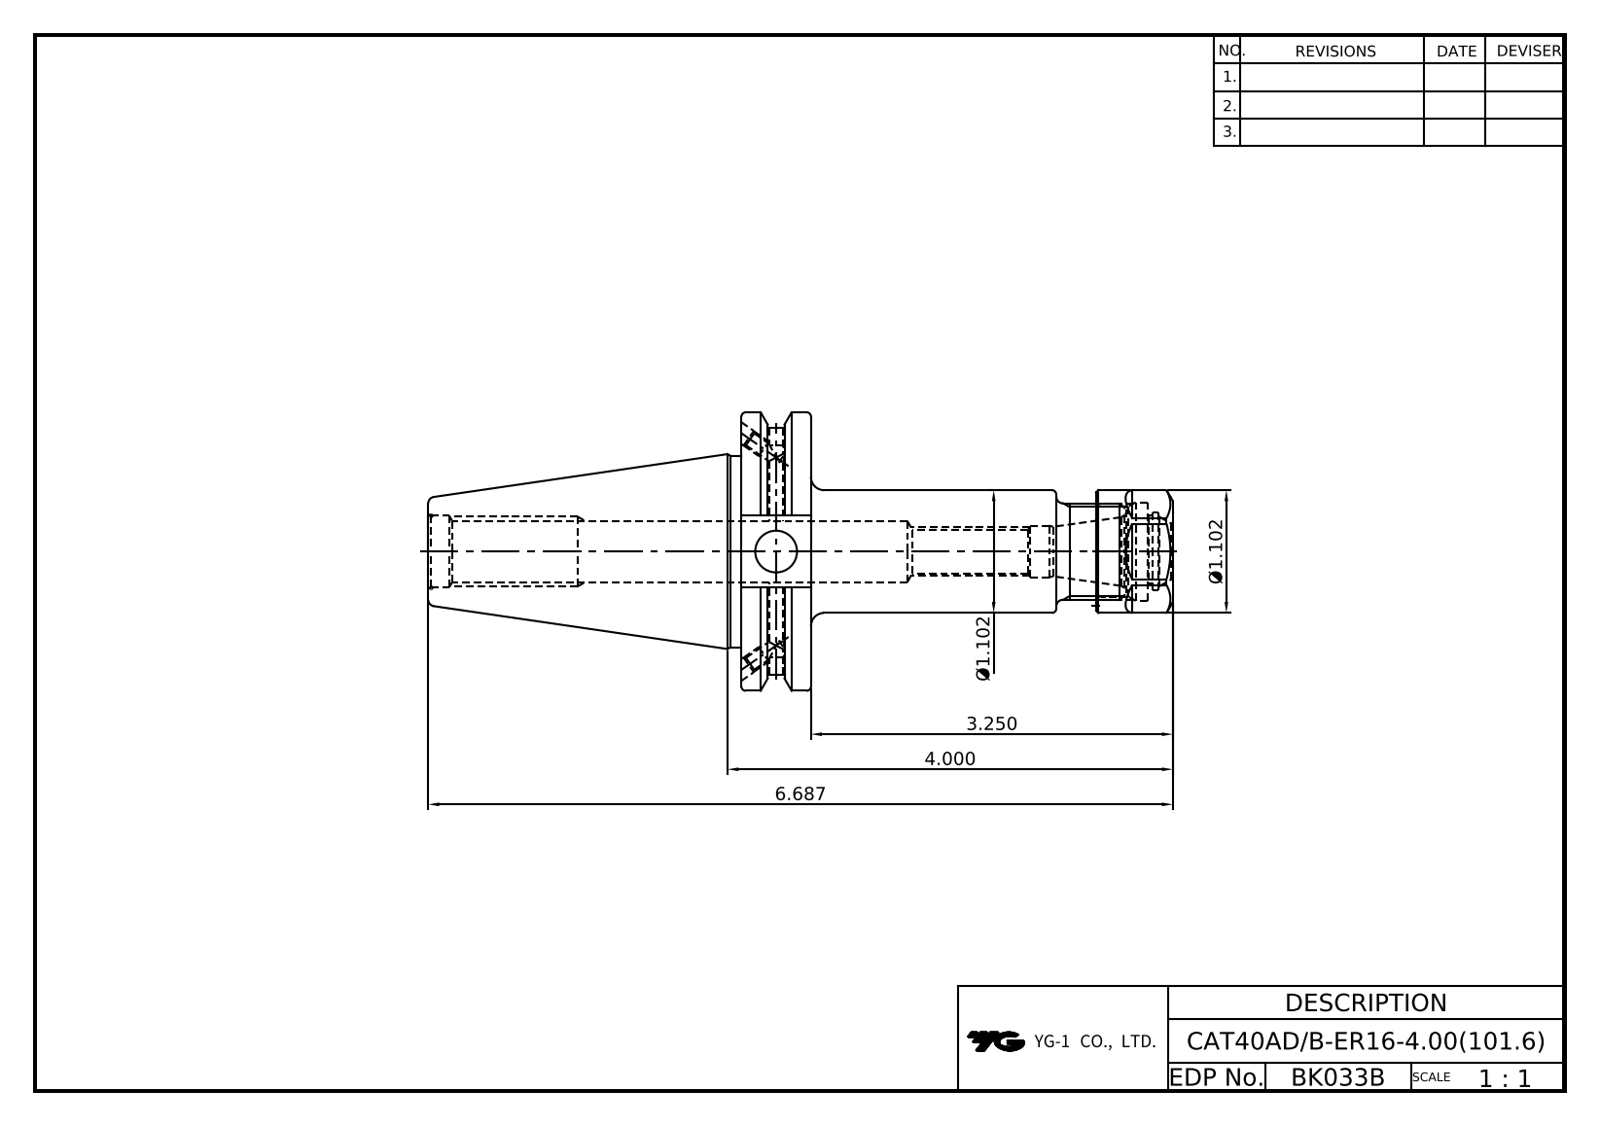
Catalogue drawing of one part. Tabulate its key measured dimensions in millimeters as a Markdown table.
| quantity | value |
| --- | --- |
| part name | LO-CAT40ADB-ER16-4.00; ER16NUT |
| STEP written by | Autodesk Inventor 2022 (AUTOMOTIVE_DESIGN) |
| units | millimeters |
| bodies | 2 solids, 125 faces (56 planar, 38 cylindrical, 31 other) |
| overall size | 169.85 × 63.5 × 61.09 |
| volume | 138 444 mm³ |
| surface area | 33 152 mm² |
| round holes (diameter × count) | 3.24 × 4, 4 × 2, 4.2 × 2, 1 × 1, 9.4 × 1, 9.53 × 1, 11.8 × 1, 12.8 × 1, 13 × 1, 13.39 × 1, 16.3 × 1, 17.7 × 1 |
| round bosses / shafts (diameter × count) | 63.5 × 1, 43.6 × 1, 28 × 1, 22 × 1 |
| partial cylindrical surfaces (radius × count) | 7.7 × 2, 28.15 × 1 |
| main face-to-face distances | 15.88, 25, 98.43, 82.55, 4.31, 20.69, 92.63, 76.75, 5.8, 47.6 |
| hole center spacings | 12 |
